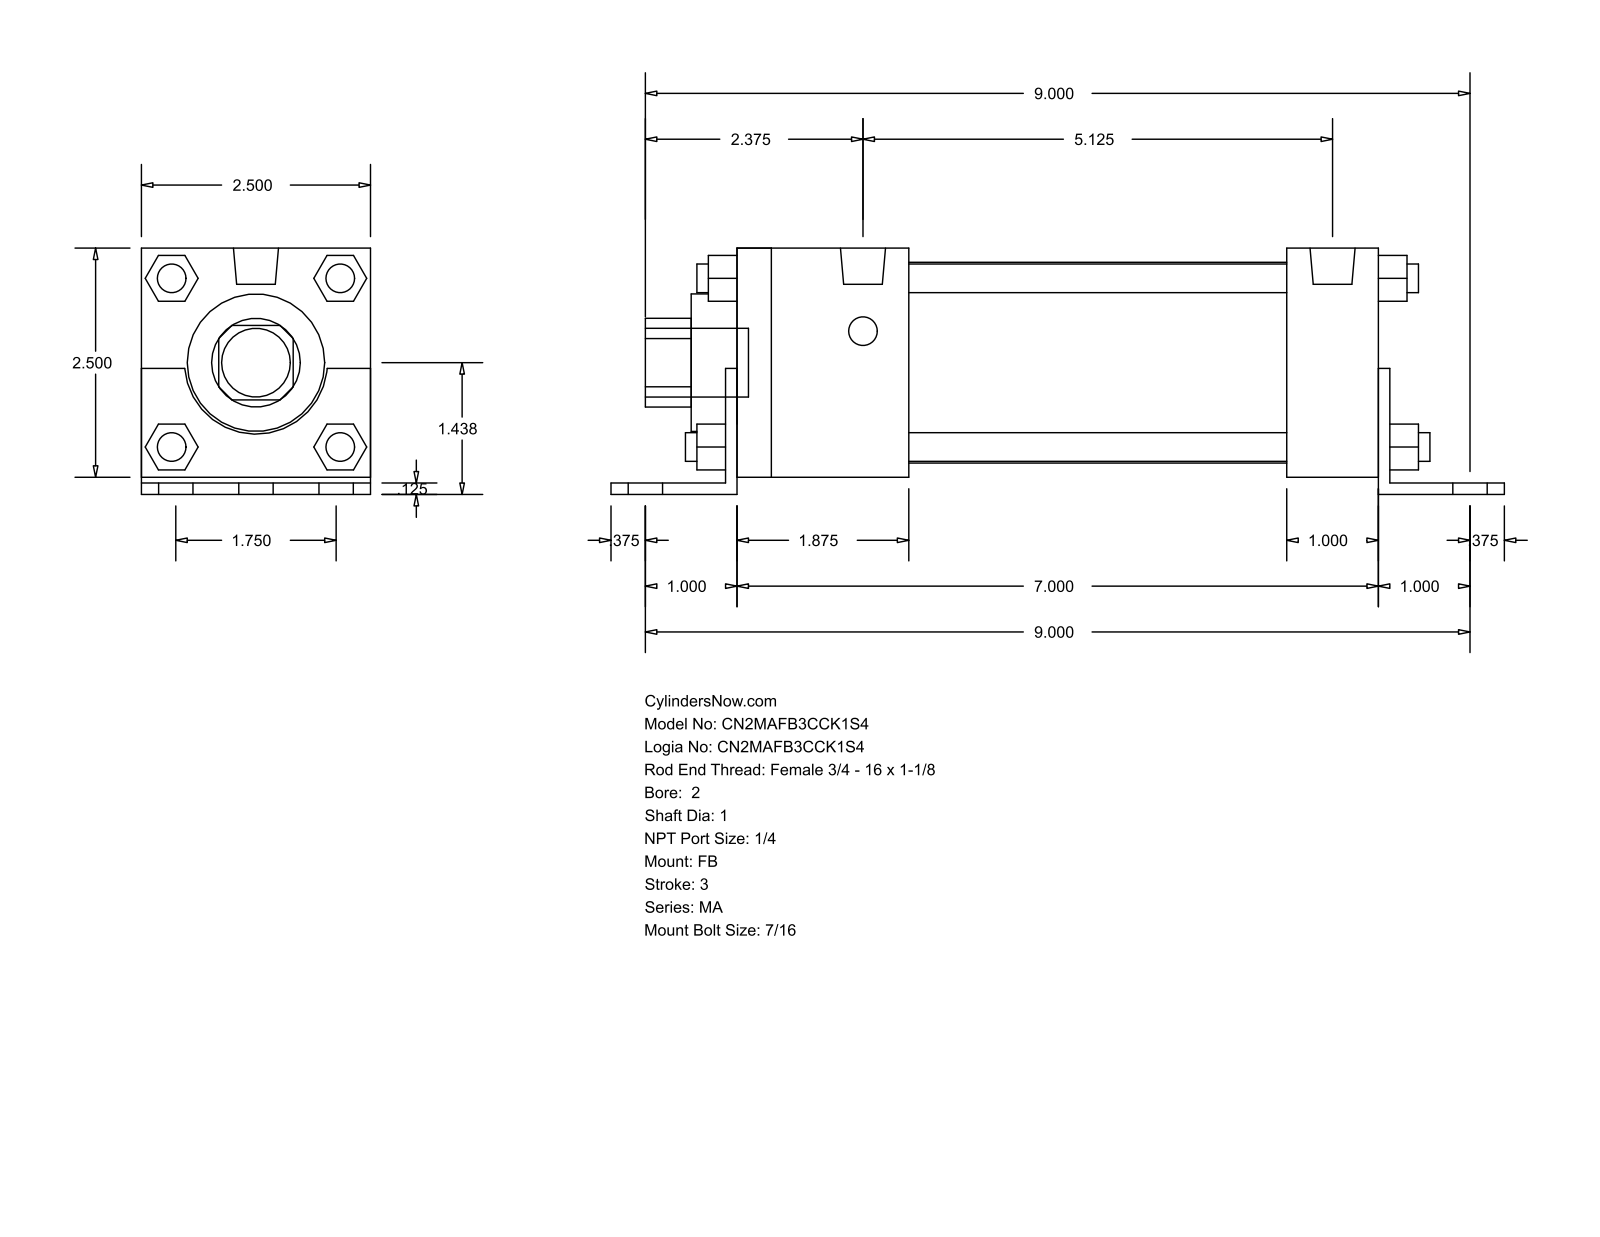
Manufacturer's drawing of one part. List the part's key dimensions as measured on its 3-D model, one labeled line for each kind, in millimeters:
Part name (STEP PRODUCT): MA_FB__0200_1
STEP written by: GSSL Pune (CONFIG_CONTROL_DESIGN)
Units: millimetres
Bodies: 0 solids, 140 faces (105 planar, 35 cylindrical, 0 other)
Overall size (bounding box): 247.65 × 68.26 × 63.5
Round holes (diameter × count): ⌀25.4 ×1, ⌀38.1 ×1, ⌀55.63 ×1
Round bosses / shafts (diameter × count): ⌀7.94 ×8, ⌀11.11 ×6, ⌀12.49 ×2, ⌀19.05 ×1
Partial cylindrical surfaces — rounded edges, fillets, slot ends (radius × count): R12.29 ×1, R19.81 ×1
Main face-to-face distances: 63.5, 3.17, 4.76, 68.26, 1.59, 65.09, 12.7, 3.18, 177.8, 180.98
